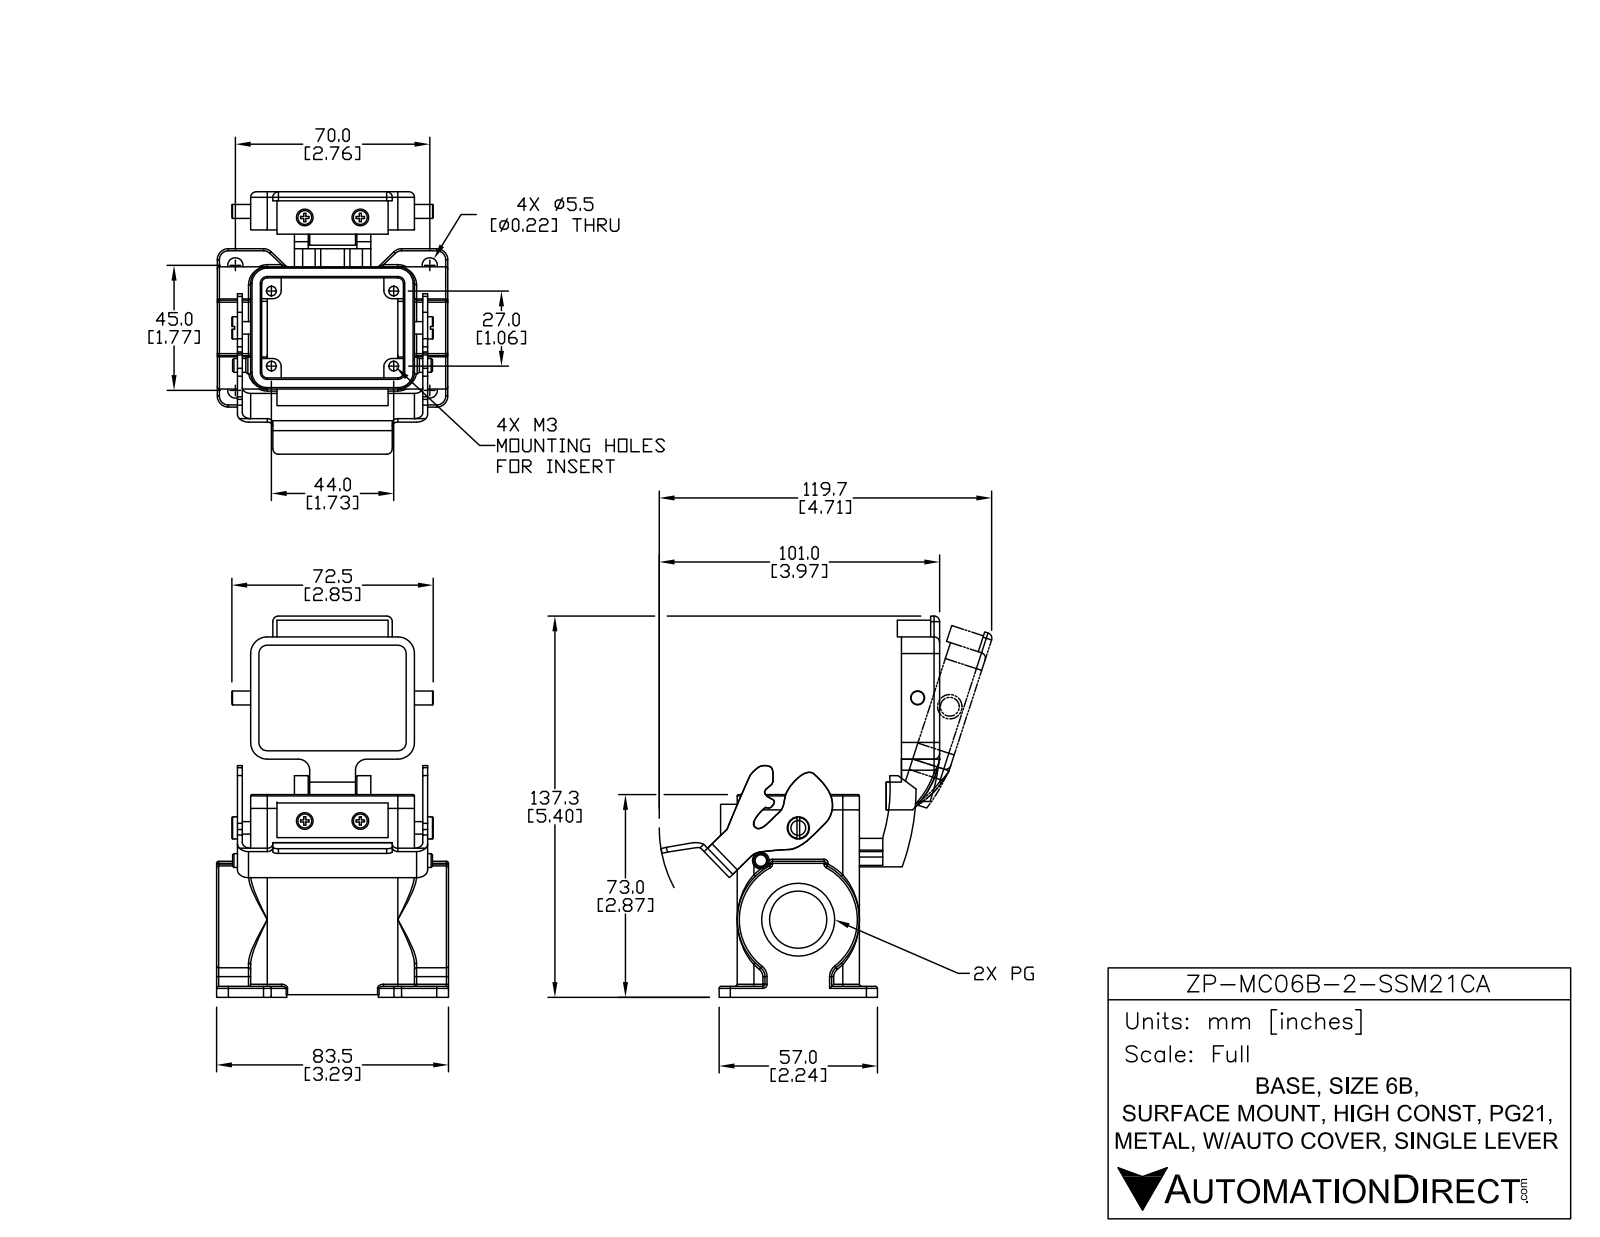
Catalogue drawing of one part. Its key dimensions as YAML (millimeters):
part_name: "ZP-MC06B-2-SSM21CA"
step_written_by: "SolidWorks 2014 (AUTOMOTIVE_DESIGN)"
units: millimeters
bodies: {solids: 11, faces: 632, planar: 246, cylindrical: 218, other: 168}
overall_size: [137.25, 94.45, 83]
volume: 133429
surface_area: 67745
round_holes:
  - {diameter: 3, count: 4}
  - {diameter: 5.5, count: 4}
  - {diameter: 4.5, count: 1}
  - {diameter: 5.32, count: 1}
  - {diameter: 20.6, count: 1}
  - {diameter: 26.25, count: 1}
round_bosses_or_shafts:
  - {diameter: 5, count: 6}
  - {diameter: 8, count: 2}
  - {diameter: 6.13, count: 1}
  - {diameter: 6, count: 1}
partial_cylinders:
  - {radius: 0.75, count: 41}
  - {radius: 2, count: 23}
  - {radius: 4, count: 14}
  - {radius: 3, count: 12}
  - {radius: 0.5, count: 8}
  - {radius: 6, count: 8}
  - {radius: 21.95, count: 2}
  - {radius: 3.75, count: 1}
face_to_face_distances: [4, 40, 3, 1.75, 44, 12, 9, 6, 1, 5]
hole_center_spacings: [13.76, 14.53, 27, 34.08, 35.93, 38, 44, 51.62]
